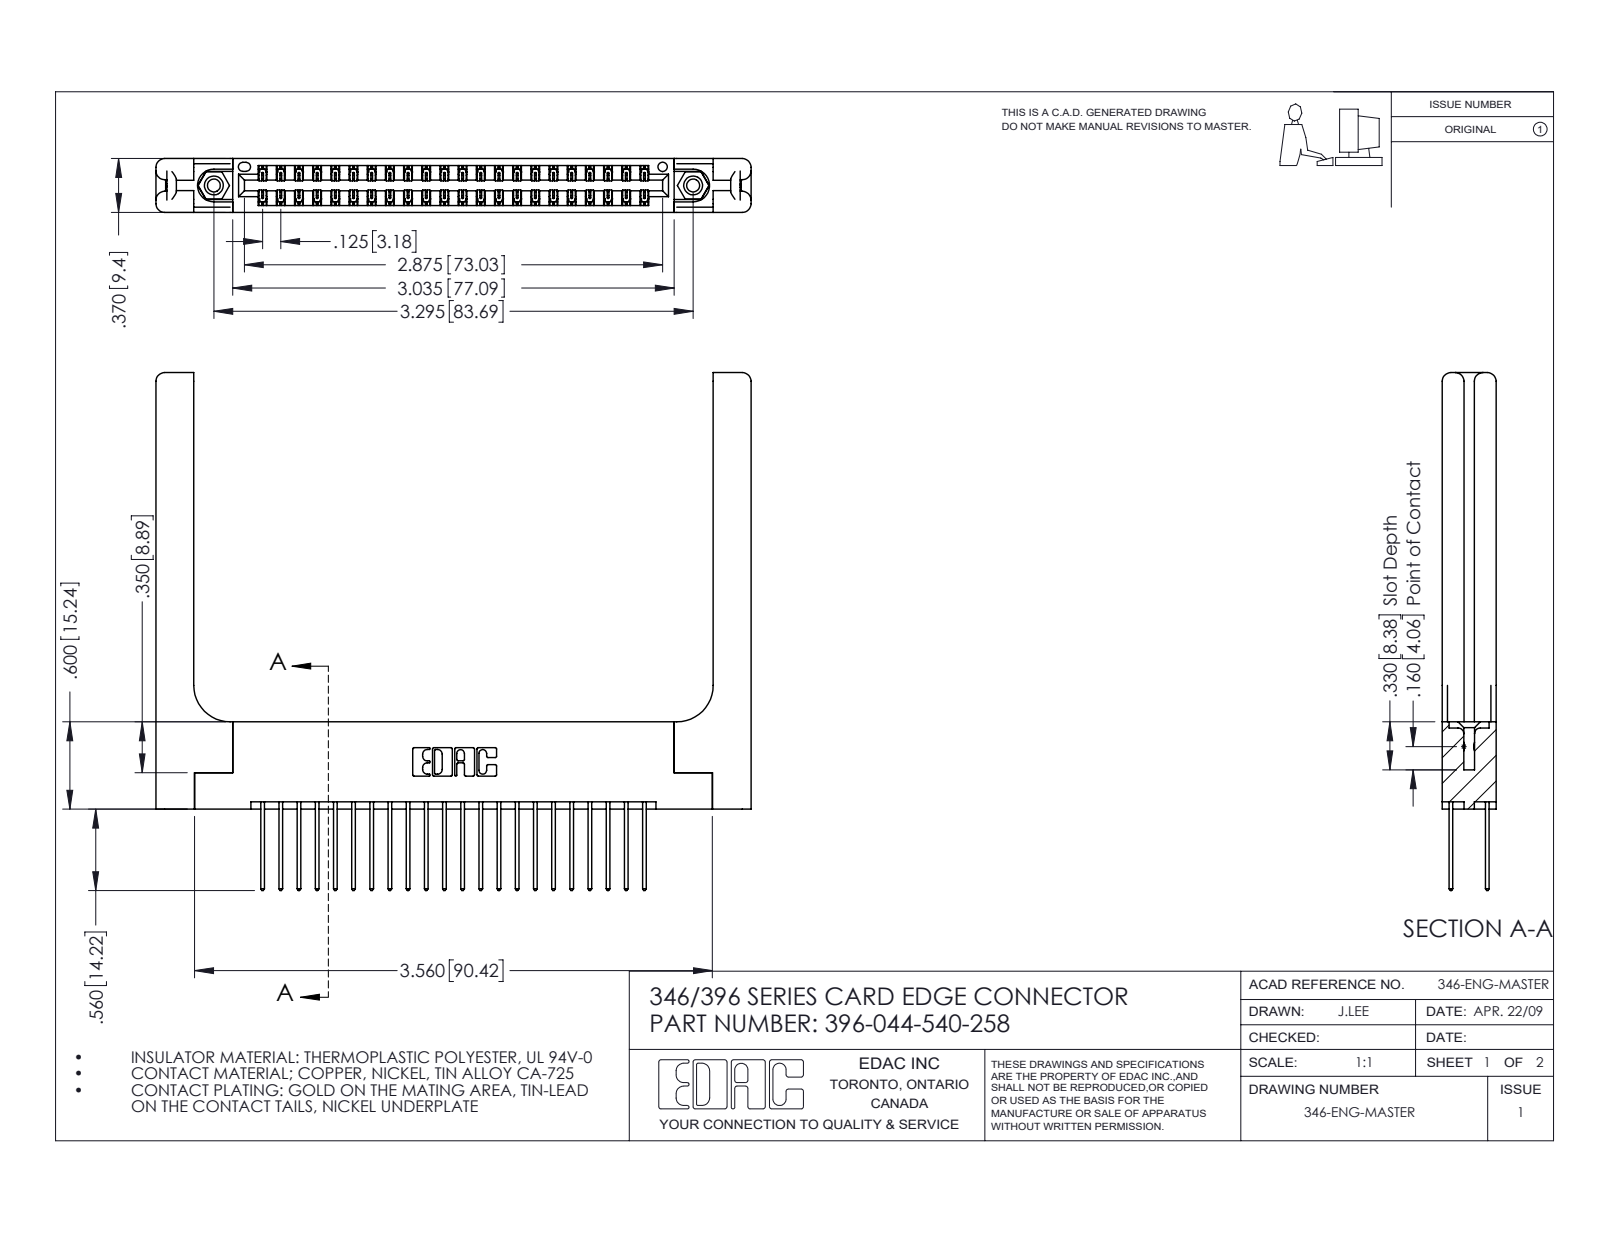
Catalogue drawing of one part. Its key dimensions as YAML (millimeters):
part_name: "346 Part_Flush Mounting Lugs - 0.156 Dia-TH; 396-044-540-258; 345-250-001_345-250-001-102; 346-220-058_345-220-058 (+1 more)"
step_written_by: "SolidWorks 2016 (CONFIG_CONTROL_DESIGN)"
units: millimeters
bodies: {solids: 49, faces: 2666, planar: 1764, cylindrical: 842, other: 60}
overall_size: [103.9, 90.4, 9.4]
volume: 17630
surface_area: 19390
round_holes:
  - {diameter: 2.3, count: 2}
  - {diameter: 3.2, count: 2}
  - {diameter: 4, count: 2}
  - {diameter: 1.6, count: 1}
round_bosses_or_shafts:
  - {diameter: 3.9, count: 2}
partial_cylinders:
  - {radius: 0.2, count: 66}
  - {radius: 0.3, count: 44}
  - {radius: 0.3, count: 22}
  - {radius: 1.5, count: 16}
  - {radius: 0.2, count: 6}
  - {radius: 0.8, count: 6}
  - {radius: 0.7, count: 3}
  - {radius: 0.4, count: 2}
face_to_face_distances: [9.4, 1.8, 1.2, 8.2, 6.4, 3.8, 3.8, 0.6, 7.6, 7]
hole_center_spacings: [6.2, 78.4, 83.7]
